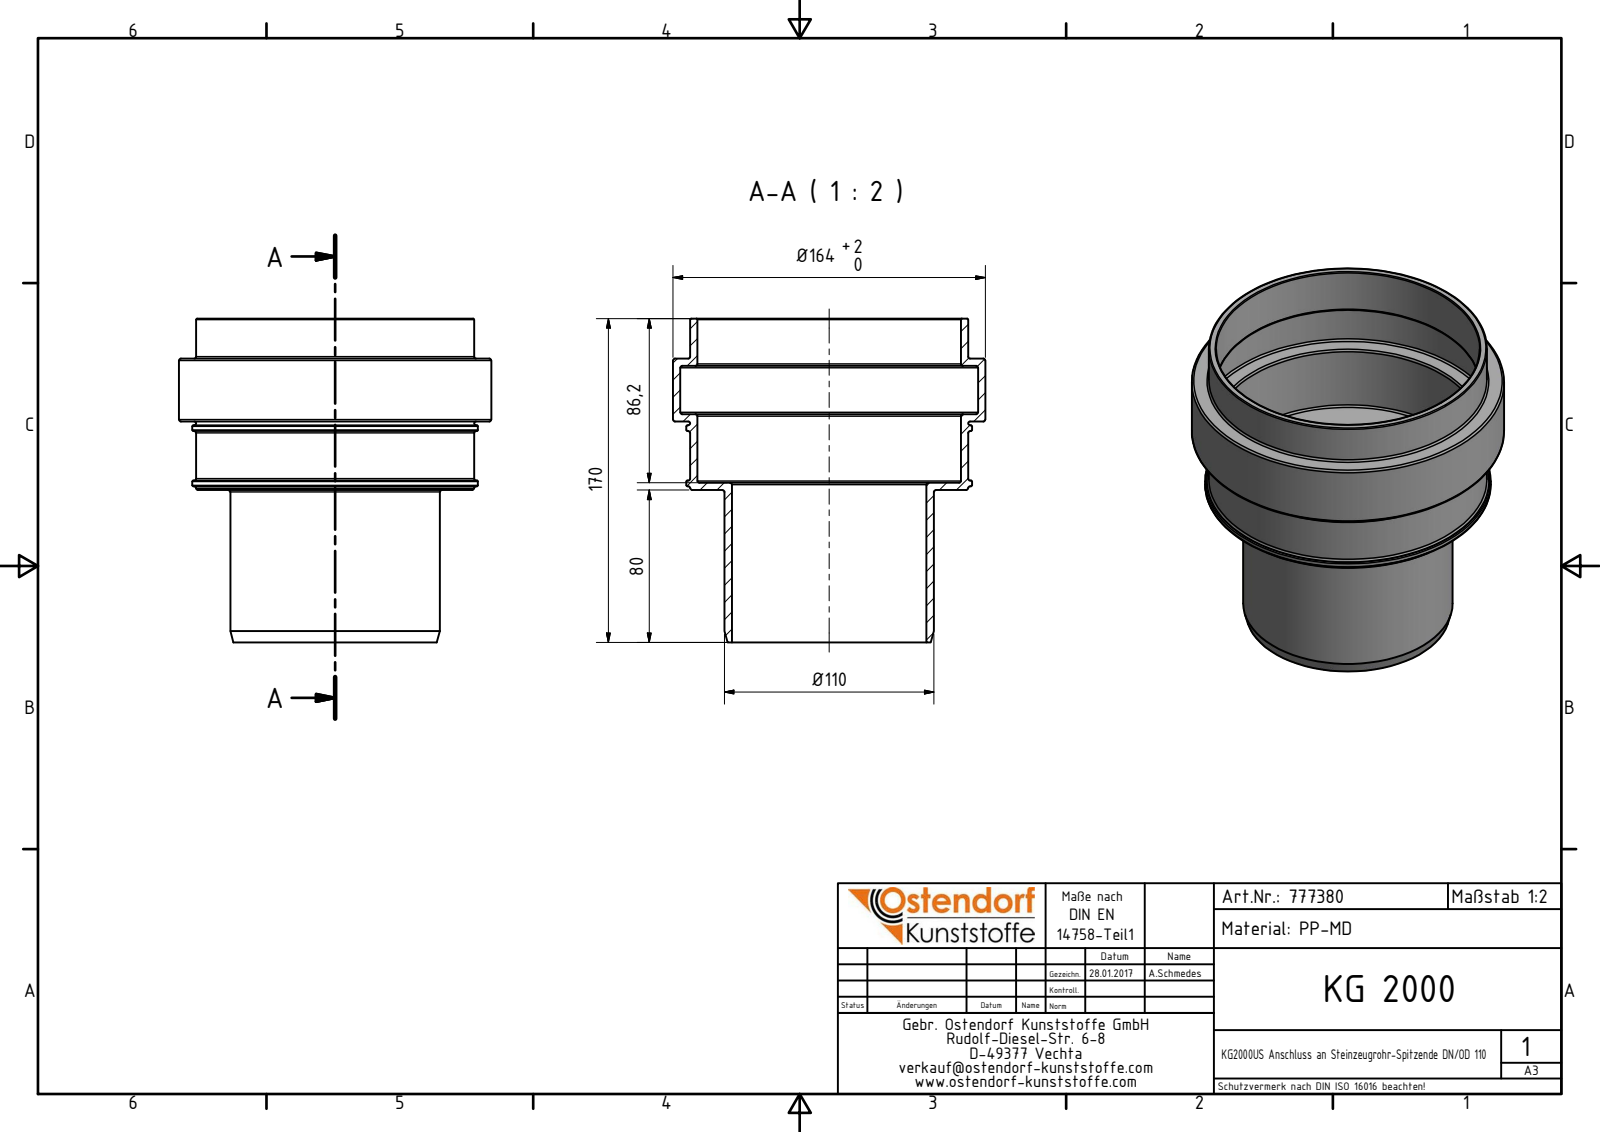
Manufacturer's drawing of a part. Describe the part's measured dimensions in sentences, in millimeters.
The part is named "777380 KG2000US Anschluss an Steinzeugrohr-Spitzende DN_OD 110". Its 3-D file was written by "Autodesk Inventor 2016 (AUTOMOTIVE_DESIGN)". It is 1 solid with 44 faces: 12 planar, 10 cylindrical and 22 other. Overall it measures 170 by 164 by 164 millimeters. Its volume is 328 403 cubic millimeters and its surface area 170 409 square millimeters. Round holes: 1 of diameter 102, 1 of diameter 138.4, 1 of diameter 156.4. Round bosses or shafts: 1 of diameter 164, 1 of diameter 150, 1 of diameter 146, 1 of diameter 110. The main face-to-face distances are 3.8, 65.2, 36, 29.2, 69, 32.2, 33, 61.4, 39.8, 25.4.
